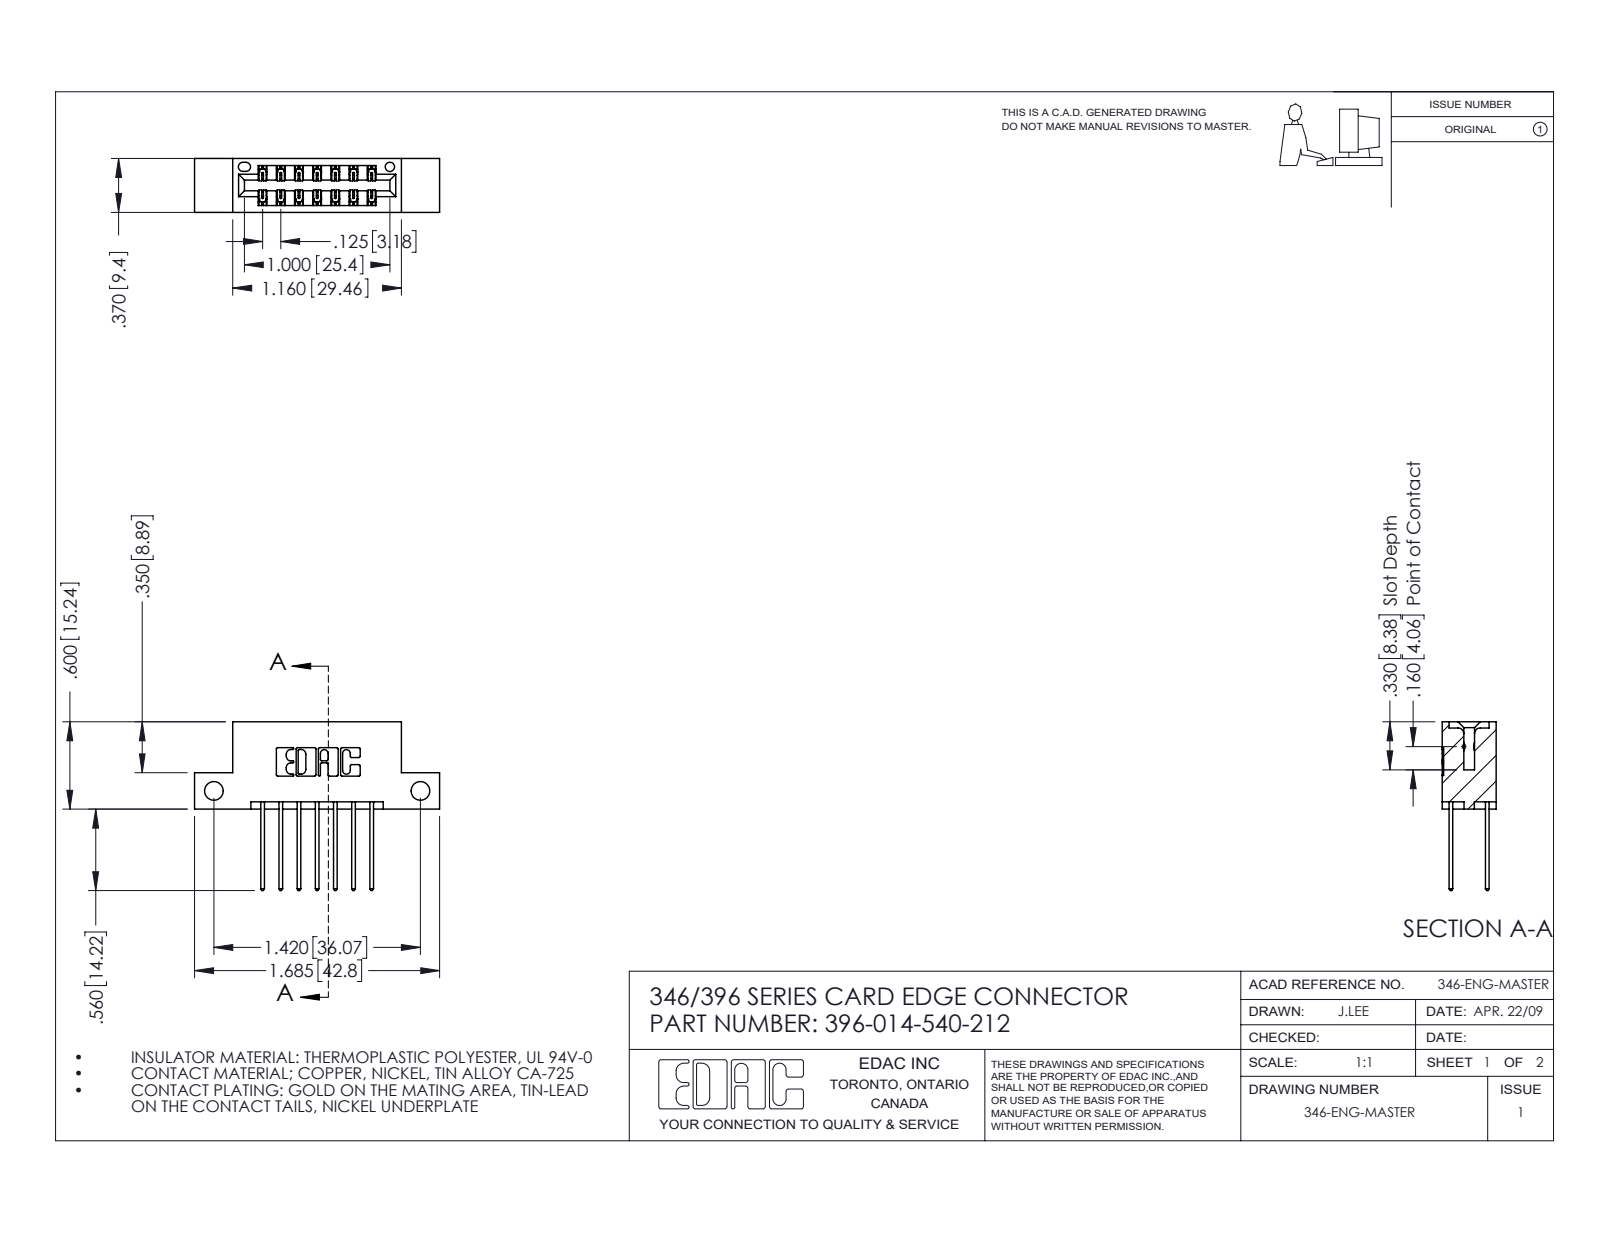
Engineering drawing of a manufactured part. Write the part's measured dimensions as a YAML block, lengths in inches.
part_name: "346 Part_Flush Mounting Lugs - Side Mount; 345-292-001_345-293-140; 396-014-540-212"
step_written_by: "SolidWorks 2016 (CONFIG_CONTROL_DESIGN)"
units: inches
bodies: {solids: 15, faces: 850, planar: 566, cylindrical: 284, other: 0}
overall_size: [1.685, 1.16, 0.37]
volume: 0.236
surface_area: 7.563
round_holes:
  - {diameter: 0.128, count: 2}
  - {diameter: 0.064, count: 1}
partial_cylinders:
  - {radius: 0.01, count: 22}
  - {radius: 0.006, count: 21}
  - {radius: 0.01, count: 14}
  - {radius: 0.007, count: 6}
  - {radius: 0.031, count: 6}
  - {radius: 0.026, count: 3}
  - {radius: 0.014, count: 2}
  - {radius: 0.022, count: 2}
face_to_face_distances: [0.25, 0.048, 0.322, 0.37, 0.025, 0.072, 0.298, 0.275, 0.148, 0.222]
hole_center_spacings: [1.42]
